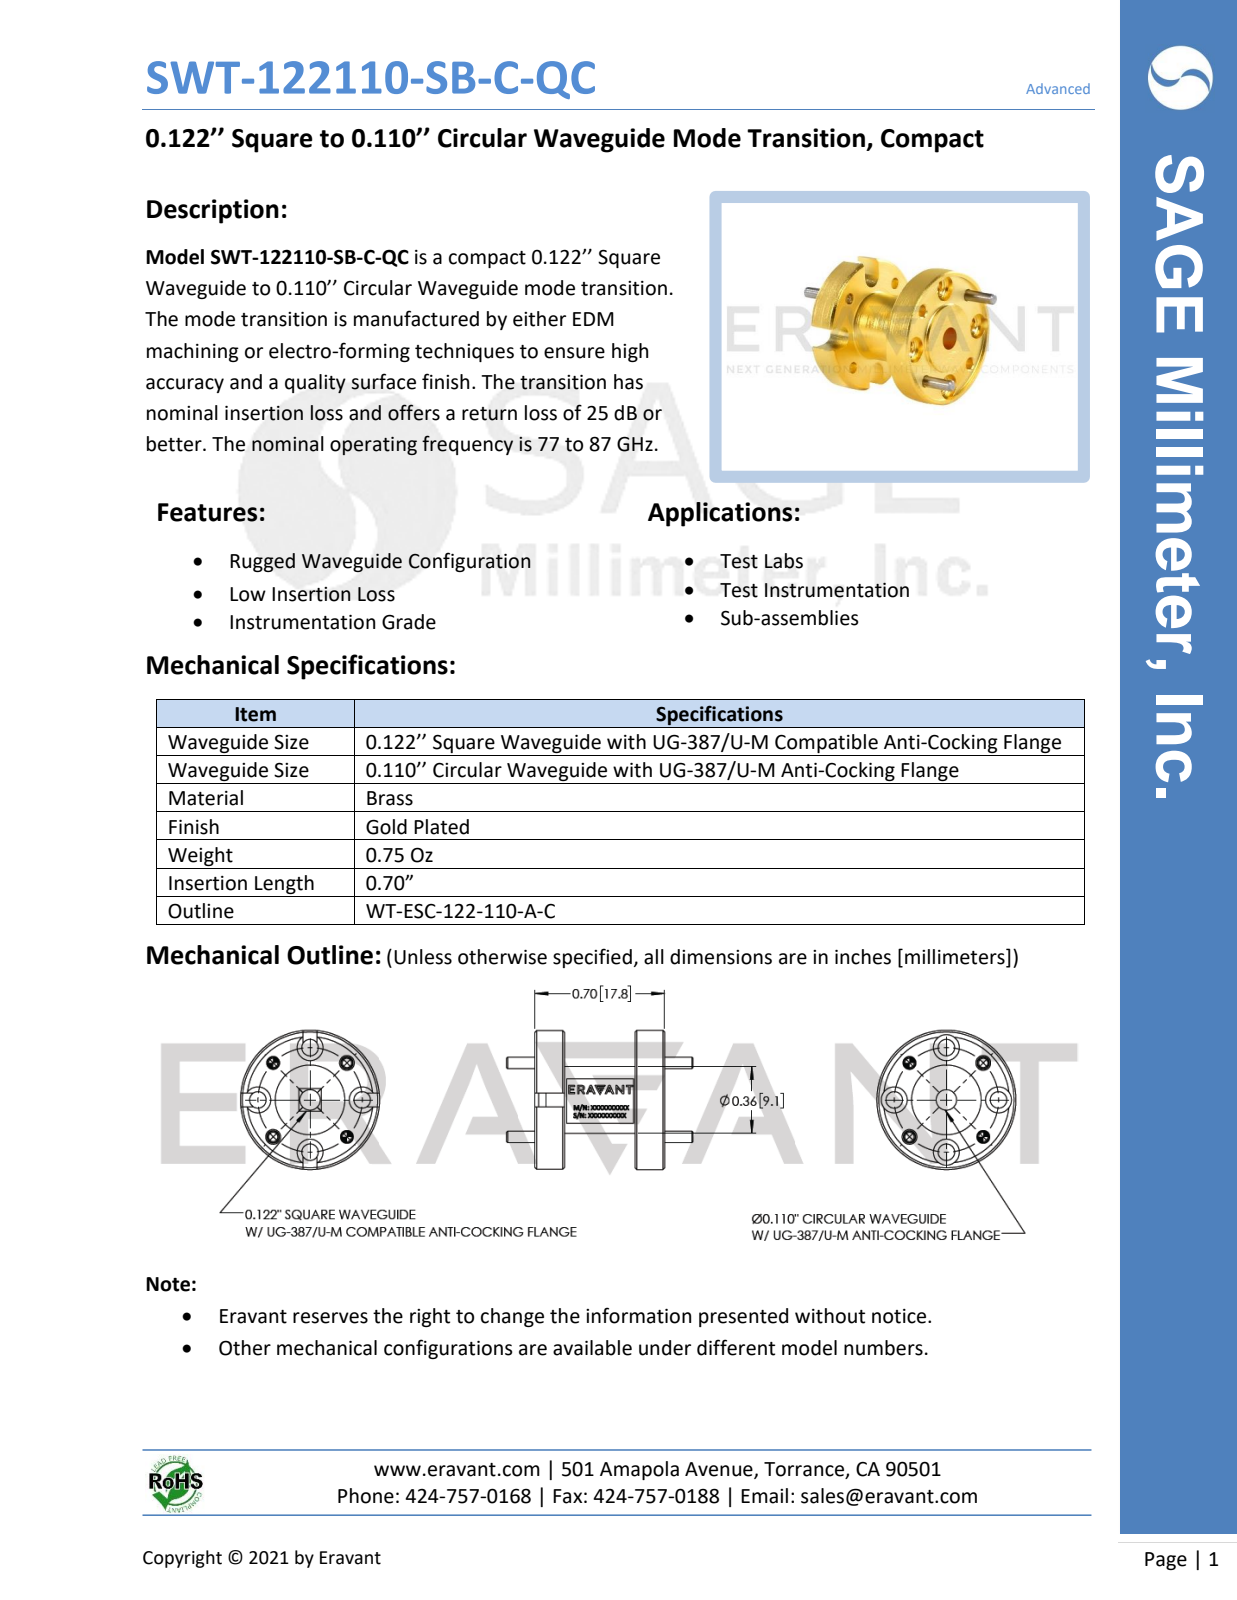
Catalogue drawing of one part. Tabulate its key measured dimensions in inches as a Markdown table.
| quantity | value |
| --- | --- |
| part name | WT-ESC-122-110-A-C, Defeatured |
| STEP written by | SolidWorks 2021 (AUTOMOTIVE_DESIGN) |
| units | inches |
| bodies | 1 solid, 159 faces (37 planar, 78 cylindrical, 44 other) |
| overall size | 1.005 × 0.75 × 0.75 |
| volume | 0.157 in³ |
| surface area | 3.261 in² |
| round holes (diameter × count) | 0.061 × 4, 0.067 × 4, 0.089 × 4, 0.14 × 4, 0.68 × 1 |
| round bosses / shafts (diameter × count) | 0.063 × 4, 0.75 × 1, 0.375 × 1, 0.36 × 1 |
| main face-to-face distances | 0.14, 0.52, 0.02, 0.16, 0.54, 0.68, 0.38, 0.66, 0.7, 0.06 |
| hole center spacings | 0.215, 0.281, 0.398, 0.519, 0.562 |
